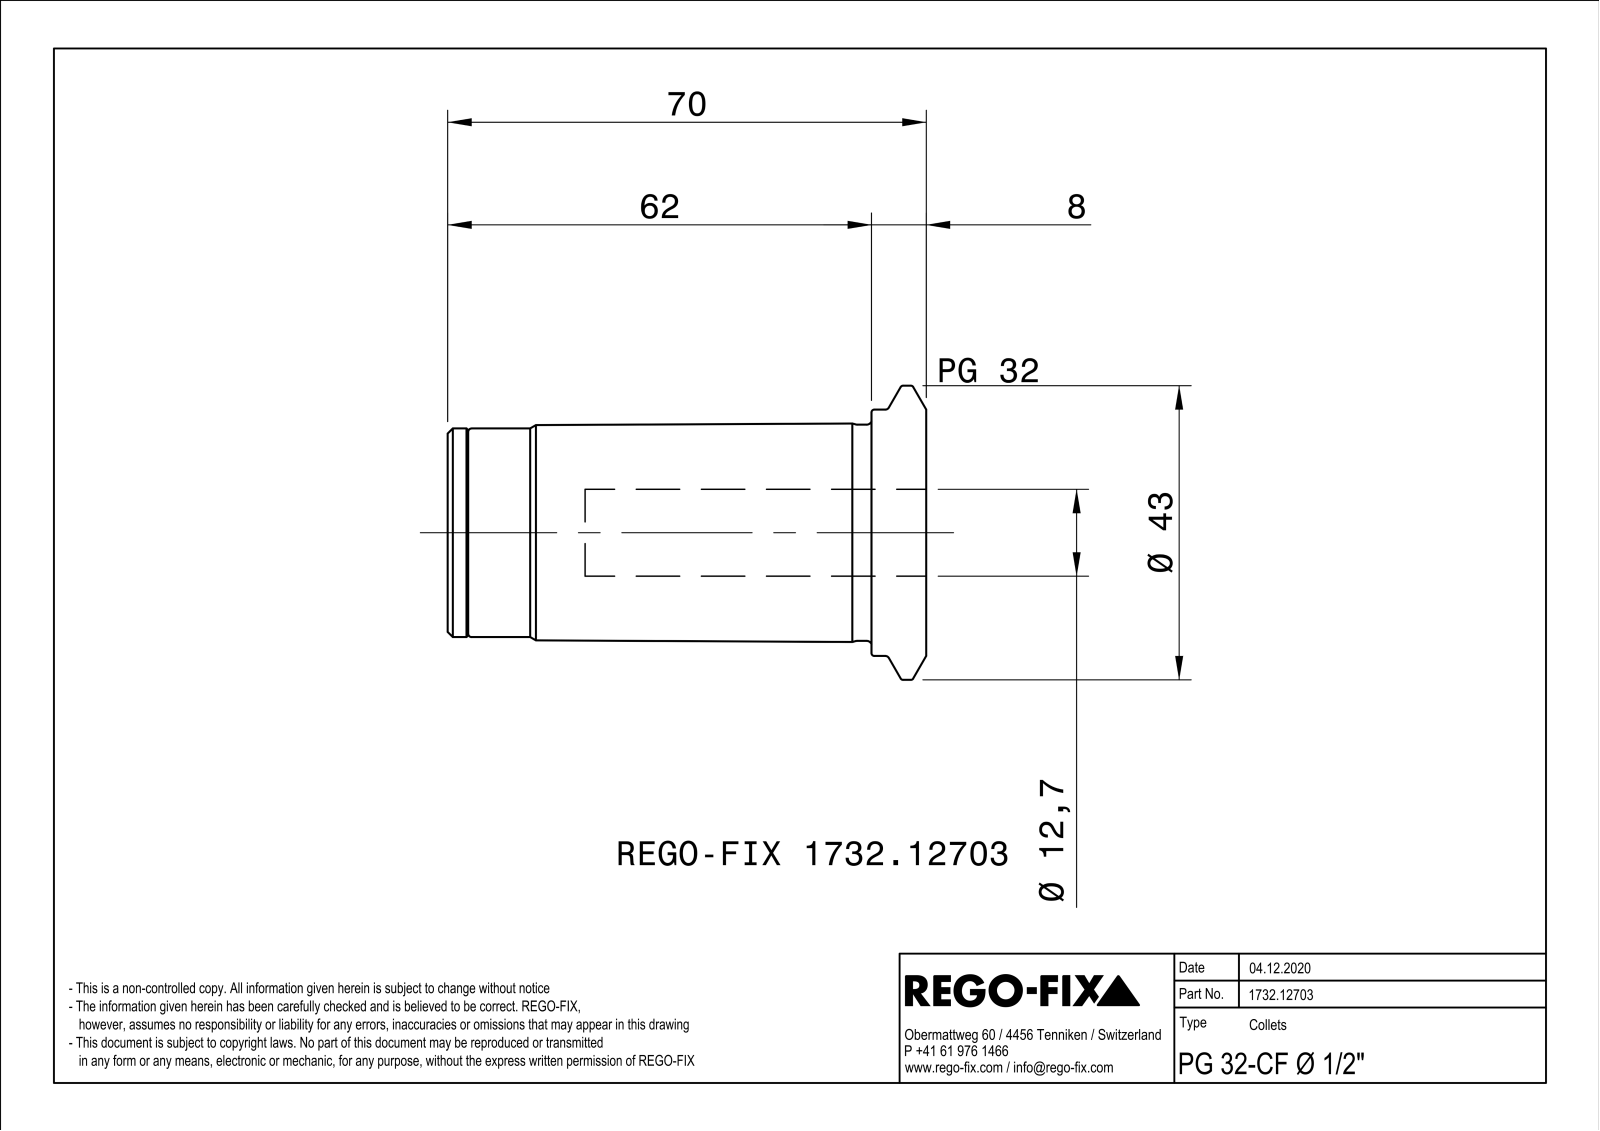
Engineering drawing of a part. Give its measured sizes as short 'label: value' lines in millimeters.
name: NOCUT
written by: SIEMENS PLM Software Solid Edge ST10 (AUTOMOTIVE_DESIGN)
unit: mm
bodies: 1 solid, 132 faces (31 planar, 46 cylindrical, 55 other)
size: 70 × 43 × 42.99
volume: 44 789 mm³; area: 16 780 mm²
holes: 3× ⌀4, 1× ⌀8.92, 1× ⌀10.5, 1× ⌀12.7, 1× ⌀15.5, 1× ⌀26.92, 1× ⌀28.5
bosses: 1× ⌀43, 1× ⌀36, 1× ⌀31.6, 1× ⌀30.5, 1× ⌀26.5, 1× ⌀21
rounds: 6× R2, 3× R1, 3× R3.5, 1× R3.98, 1× R4.75, 1× R8.75
face distances: 1, 70, 58, 12, 59, 11, 8, 60, 2, 10
hole spacings: 7.75, 13.42, 13.43
